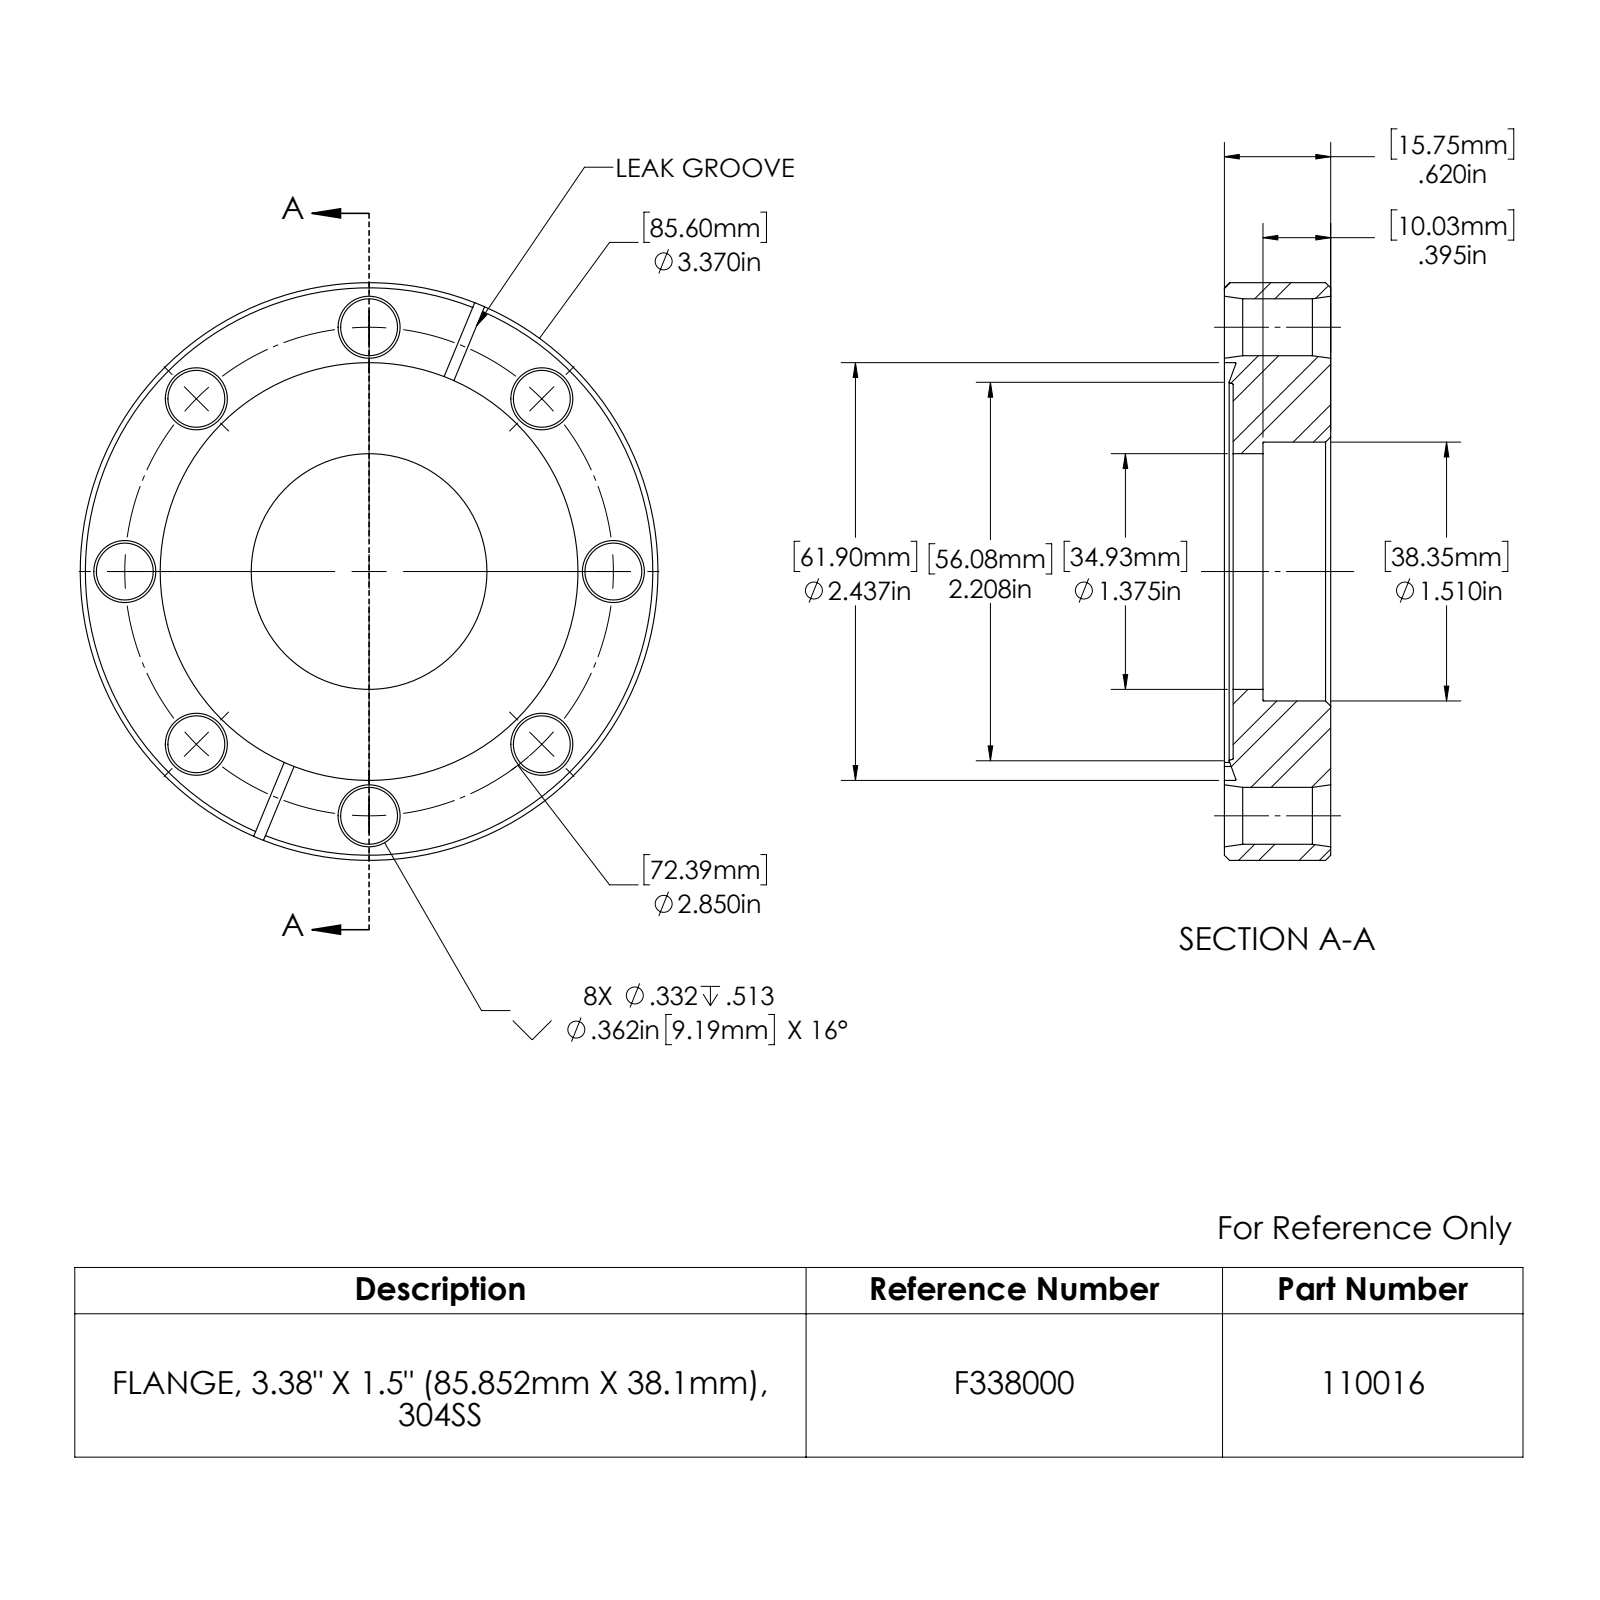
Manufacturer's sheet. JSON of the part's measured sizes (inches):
{"part_name": "110016_B", "step_written_by": "SolidWorks 2022 (CONFIG_CONTROL_DESIGN)", "units": "inches", "bodies": {"solids": 1, "faces": 86, "planar": 11, "cylindrical": 24, "other": 51}, "overall_size": [3.37, 3.37, 0.62], "volume_in3": 3.872, "surface_area_in2": 27.96, "round_holes": [[0.332, 8], [1.375, 1], [1.51, 1], [2.437, 1]], "round_bosses_or_shafts": [[3.37, 1]], "face_to_face_distances": [0.62, 0.051, 0.569, 0.225, 0.174, 0.395, 0.052, 0.173, 0.568, 0.062], "hole_center_spacings": [1.091, 2.633, 1.425, 1.425, 2.015, 2.015, 2.85, 2.85]}
